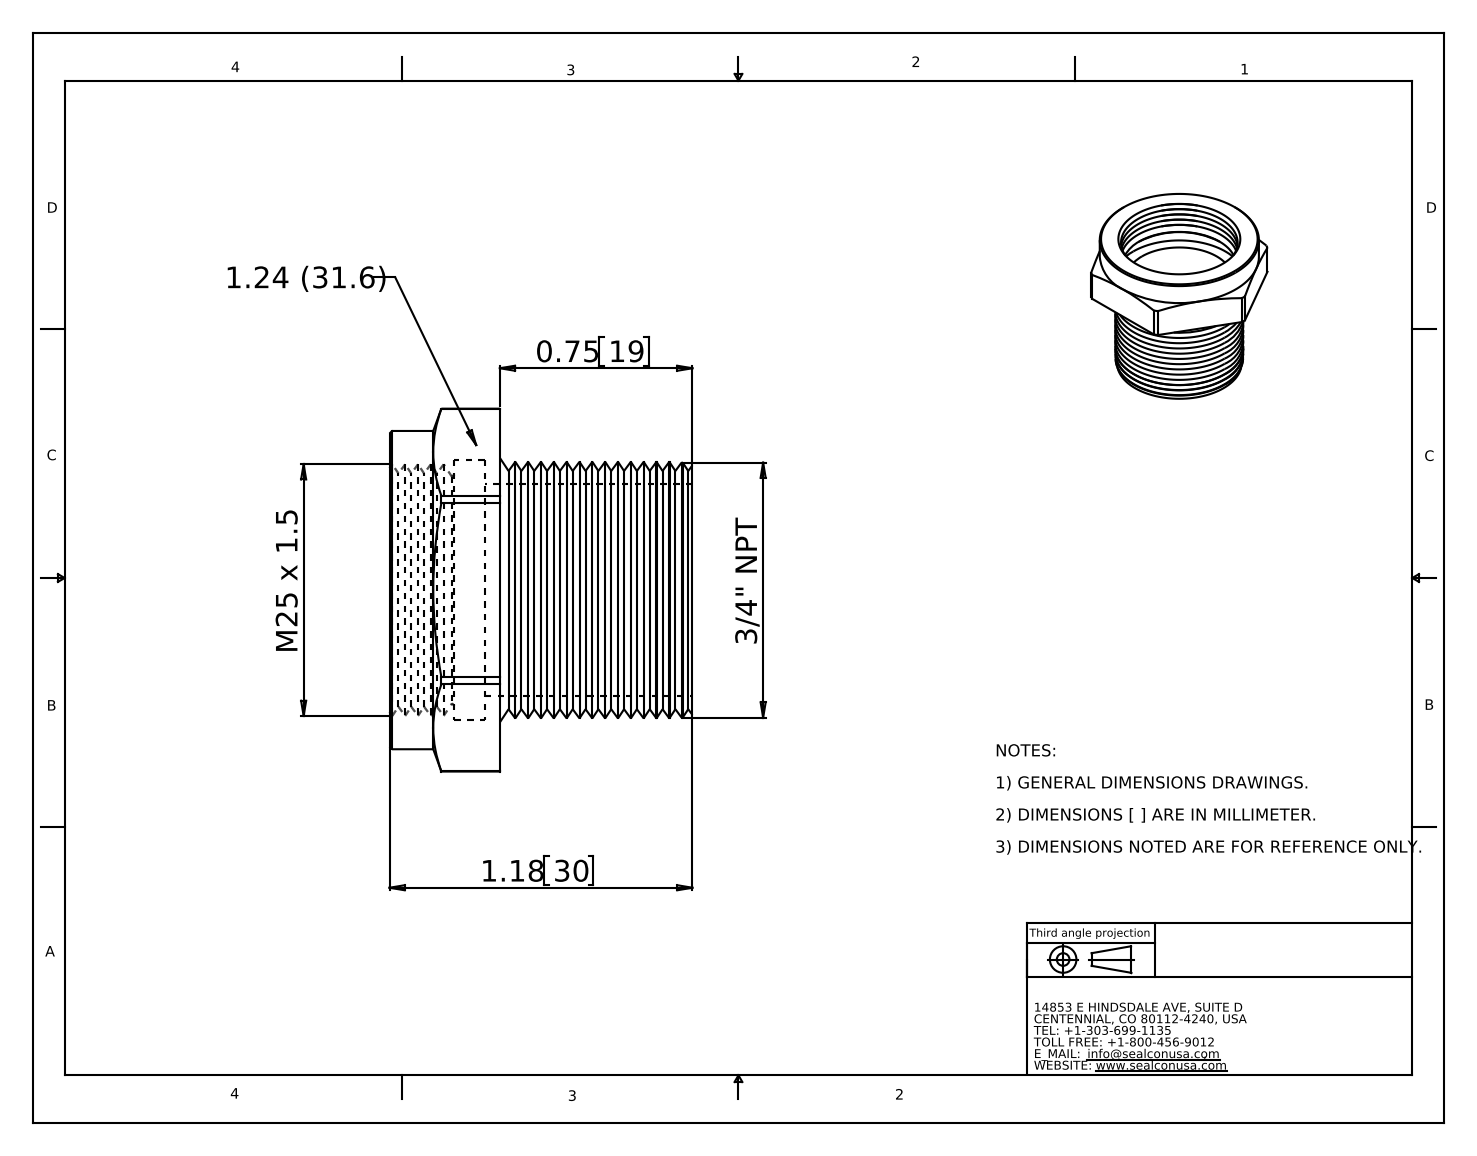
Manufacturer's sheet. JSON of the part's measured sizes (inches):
{"part_name": "AT-3425-BR", "step_written_by": "SolidWorks 2008 (CONFIG_CONTROL_DESIGN)", "units": "inches", "bodies": {"solids": 1, "faces": 121, "planar": 11, "cylindrical": 13, "other": 97}, "overall_size": [1.414, 1.24, 1.18], "volume_in3": 0.395, "surface_area_in2": 11.19, "round_holes": [[0.824, 1], [1.014, 1]], "round_bosses_or_shafts": [[1.24, 1]], "partial_cylinders_radius": [[0.707, 1]], "face_to_face_distances": [1.24, 0.43, 0.059, 0.371, 0.75, 0.809, 1.18, 0.927, 0.177, 0.118]}
